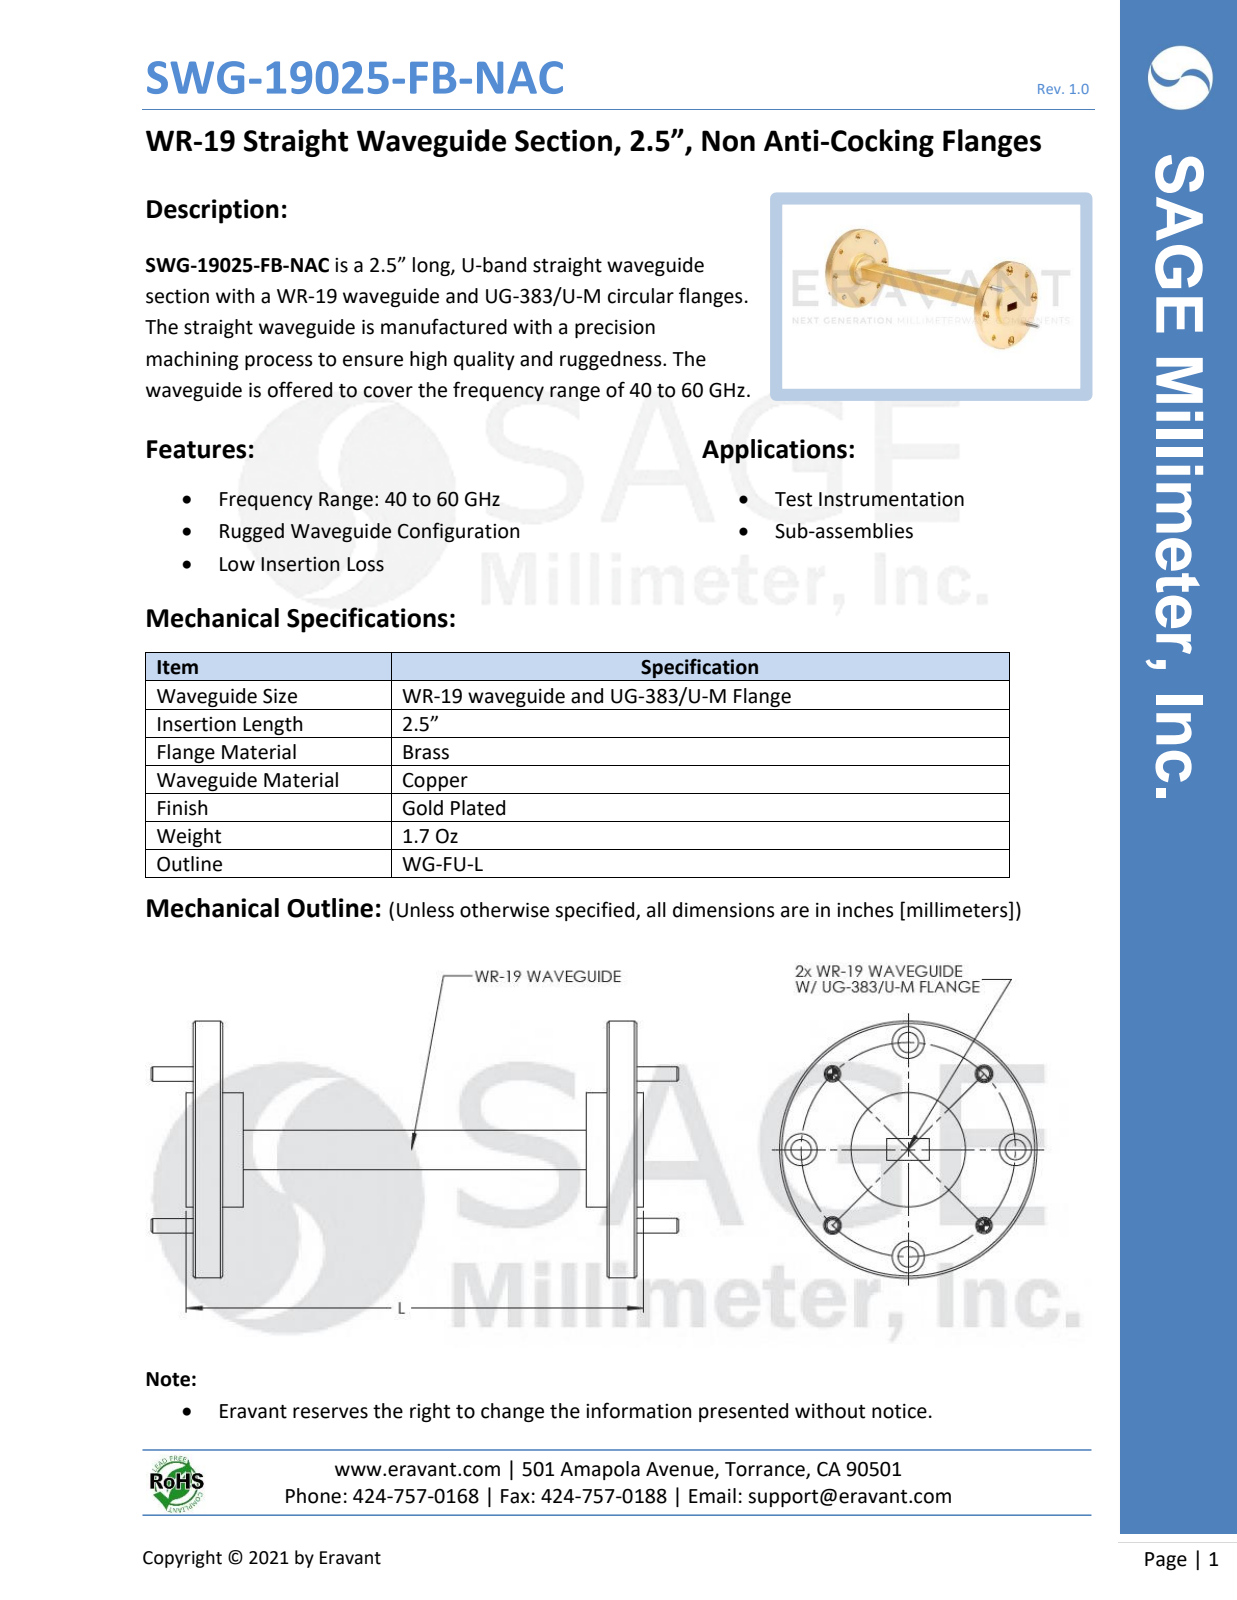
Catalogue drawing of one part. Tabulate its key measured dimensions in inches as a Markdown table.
| quantity | value |
| --- | --- |
| part name | SWG-19025-FB |
| STEP written by | SolidWorks 2021 (CONFIG_CONTROL_DESIGN) |
| units | inches |
| bodies | 5 solids, 146 faces (38 planar, 68 cylindrical, 40 other) |
| overall size | 2.805 × 1.125 × 1.125 |
| volume | 0.39 in³ |
| surface area | 7.509 in² |
| round holes (diameter × count) | 0.061 × 4, 0.067 × 4, 0.089 × 4, 0.14 × 4 |
| round bosses / shafts (diameter × count) | 0.063 × 4, 1.125 × 1, 0.5 × 1 |
| main face-to-face distances | 0.13, 2.31, 2.18, 2.44, 0.174, 0.03, 0.16, 2.34, 2.47, 0.268 |
| hole center spacings | 0.359, 0.663, 0.866, 0.938 |
